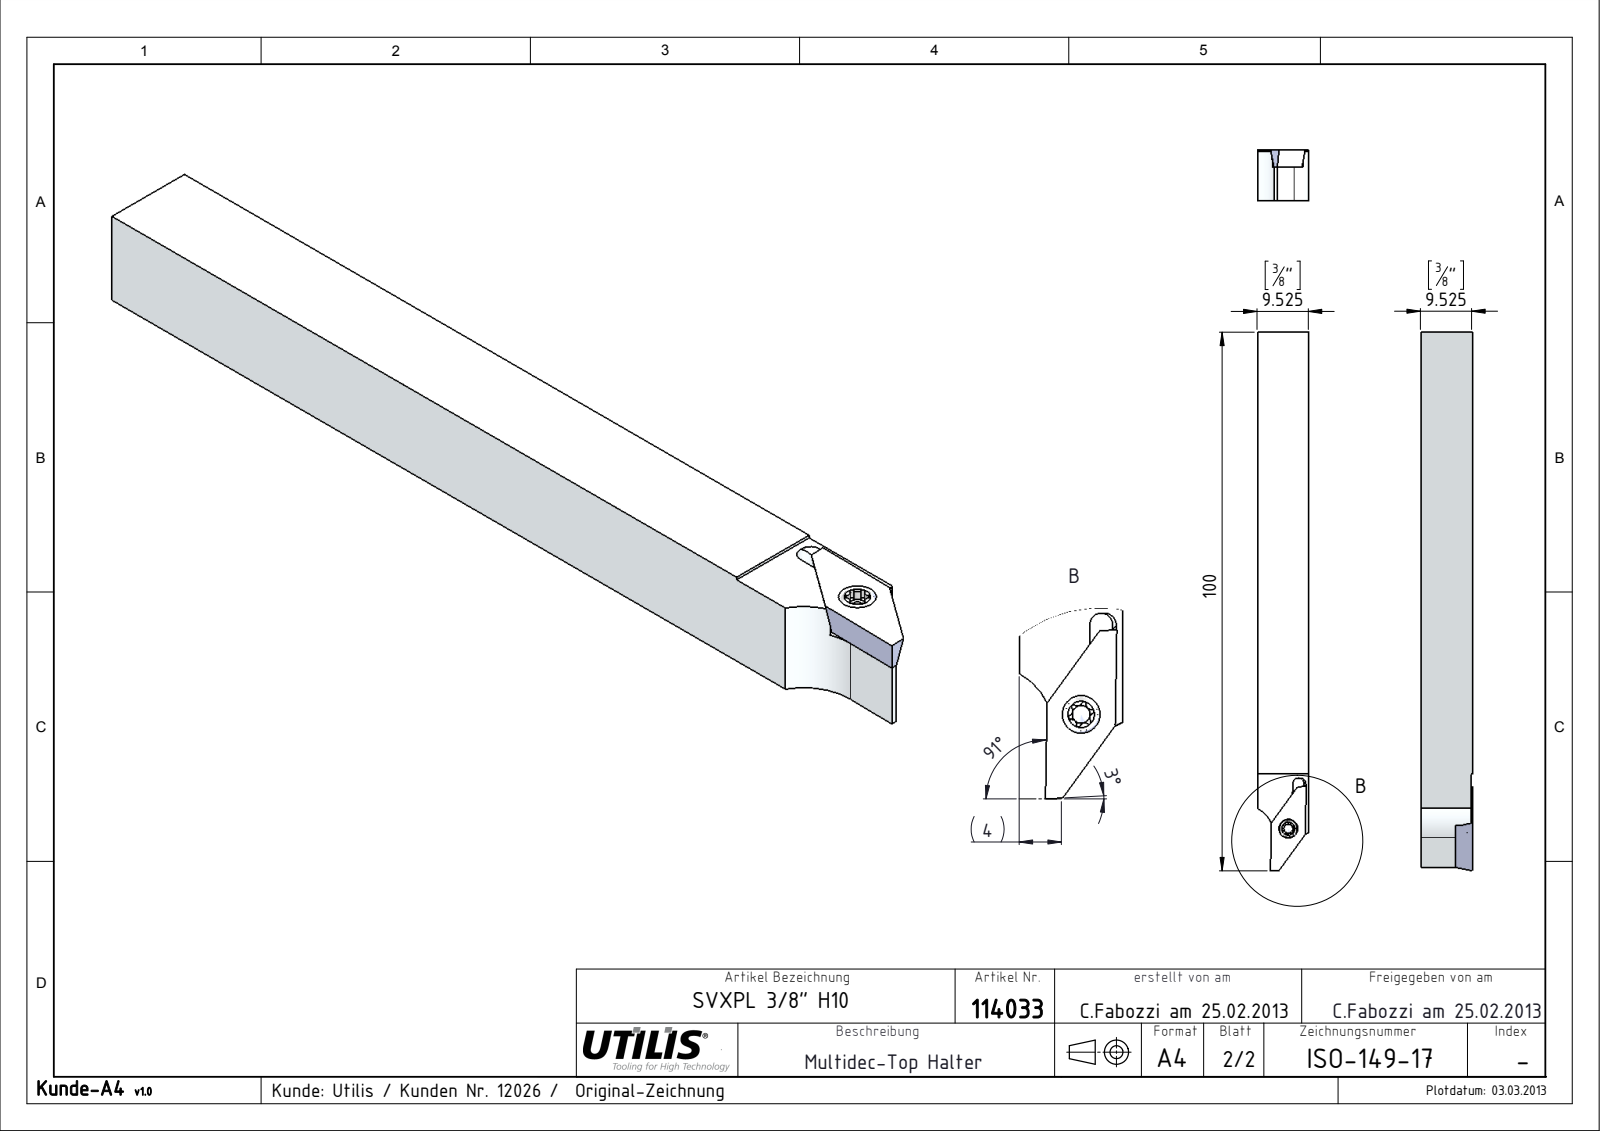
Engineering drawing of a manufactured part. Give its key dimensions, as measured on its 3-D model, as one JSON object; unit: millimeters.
{"part_name": "ISO-149-Kunde_17; MSP-7_M2,5X6-TX8 CERATIZIT Schraube; VPGT 10 L_01; ISO-149-17", "step_written_by": "SolidWorks 2015 (CONFIG_CONTROL_DESIGN)", "units": "millimeters", "bodies": {"solids": 3, "faces": 71, "planar": 27, "cylindrical": 27, "other": 17}, "overall_size": [100, 9.53, 9.53], "volume_mm3": 8492, "surface_area_mm2": 4159, "round_holes": [[2.05, 1], [3, 1]], "round_bosses_or_shafts": [[3.45, 1], [2.5, 1]], "partial_cylinders_radius": [[0.2, 6], [0.45, 6], [6, 2], [1.05, 1]], "face_to_face_distances": [9.52, 9.53, 6.35, 3.18, 9.23, 2.88, 5.33, 2.1, 3.23, 5.32]}
